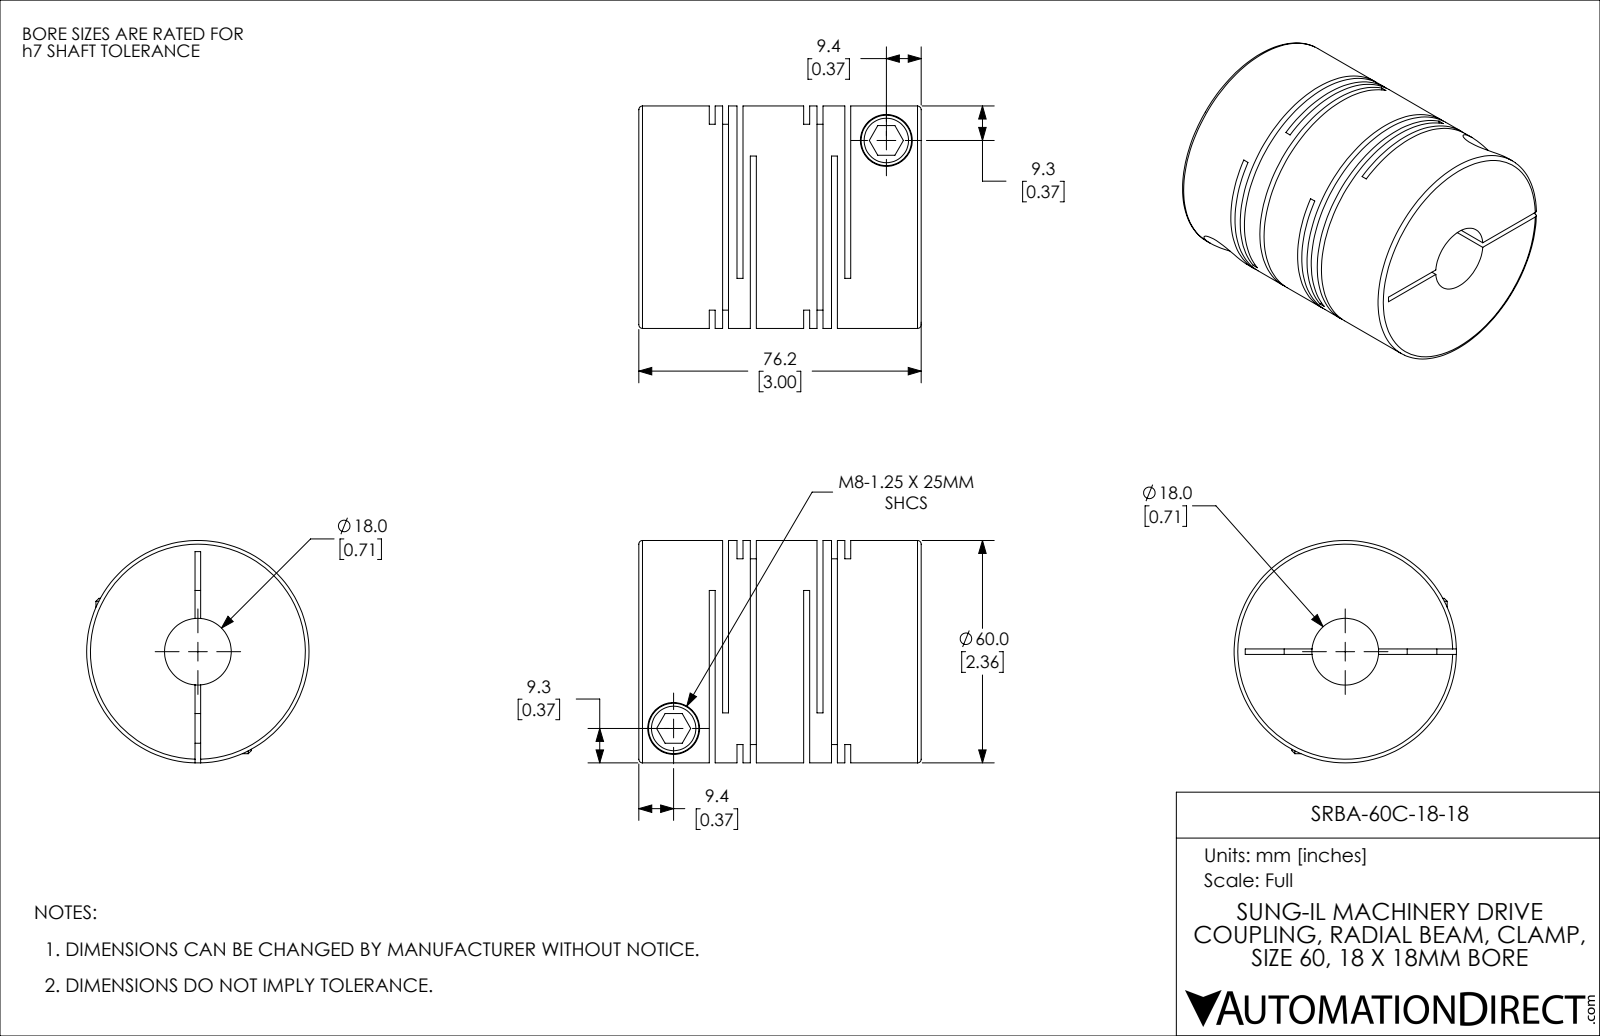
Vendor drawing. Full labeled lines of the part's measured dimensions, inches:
Part name (STEP PRODUCT): SRBA-60C-18-18
STEP written by: SolidWorks 2021 (CONFIG_CONTROL_DESIGN)
Units: inches
Bodies: 1 solid, 115 faces (60 planar, 42 cylindrical, 13 other)
Overall size (bounding box): 3 × 2.362 × 2.362
Volume: 10.01 in³ · Surface area: 92.9 in²
Round holes (diameter × count): ⌀0.315 ×2, ⌀0.551 ×2, ⌀0.709 ×1
Round bosses / shafts (diameter × count): ⌀0.535 ×2, ⌀2.362 ×1
Main face-to-face distances: 0.063, 0.142, 0.295, 1.004, 1.299, 0.232, 0.941, 0.709, 0.079, 0.154
